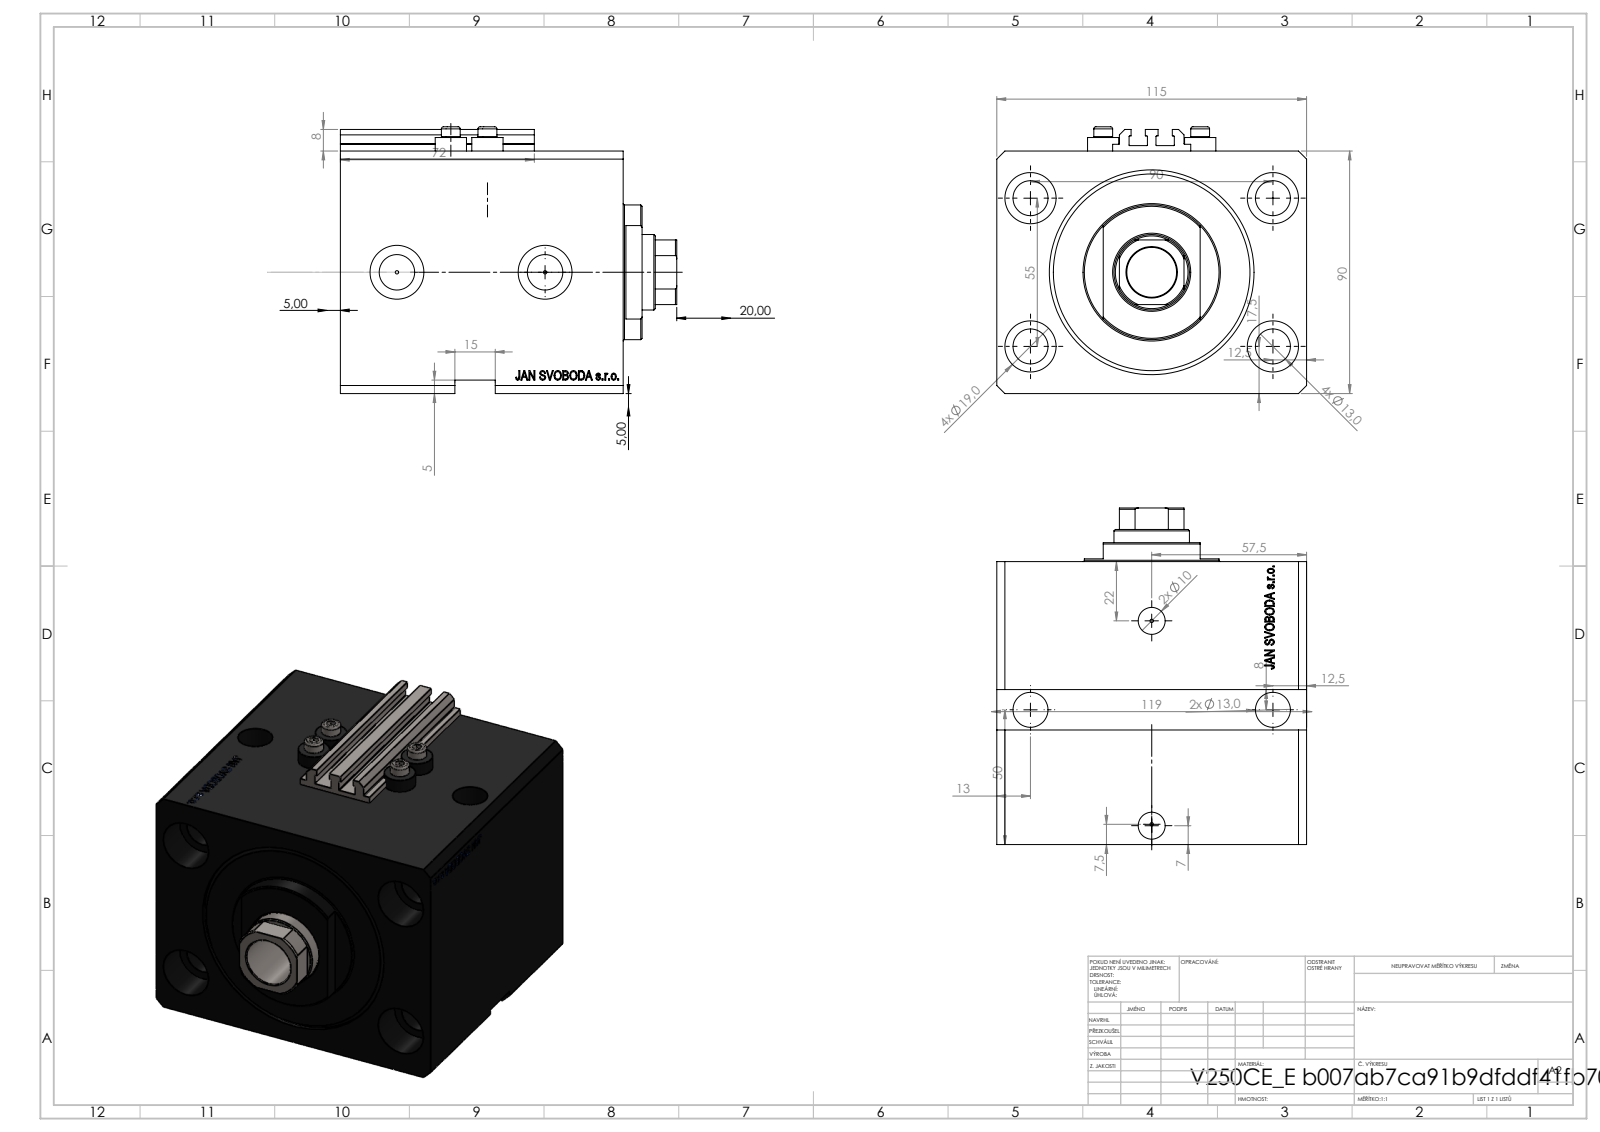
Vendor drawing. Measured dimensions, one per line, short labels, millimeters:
name: V250CE_VC_E; V250CE_C_VCP; V250CE_E_Body; ALLEN BOLT V250CE
written by: SolidWorks 2019 (CONFIG_CONTROL_DESIGN)
unit: mm
bodies: 8 solids, 1107 faces (543 planar, 126 cylindrical, 438 other)
size: 124.9 × 115 × 99
volume: 954 523 mm³; area: 156 491 mm²
holes: 6× ⌀13, 4× ⌀1.25, 4× ⌀4, 4× ⌀19, 2× ⌀10, 2× ⌀13.16, 2× ⌀20, 1× ⌀18.5, 1× ⌀28, 1× ⌀63, 1× ⌀76
bosses: 4× ⌀11.6, 4× ⌀7, 1× ⌀50
rounds: 10× R0.2, 1× R13.5
face distances: 90, 115, 105, 87.1, 17.9, 57, 74.9, 30.1, 20, 54.9
hole spacings: 52.74, 55, 90, 13.6, 27.39, 28.46, 33.62, 36
